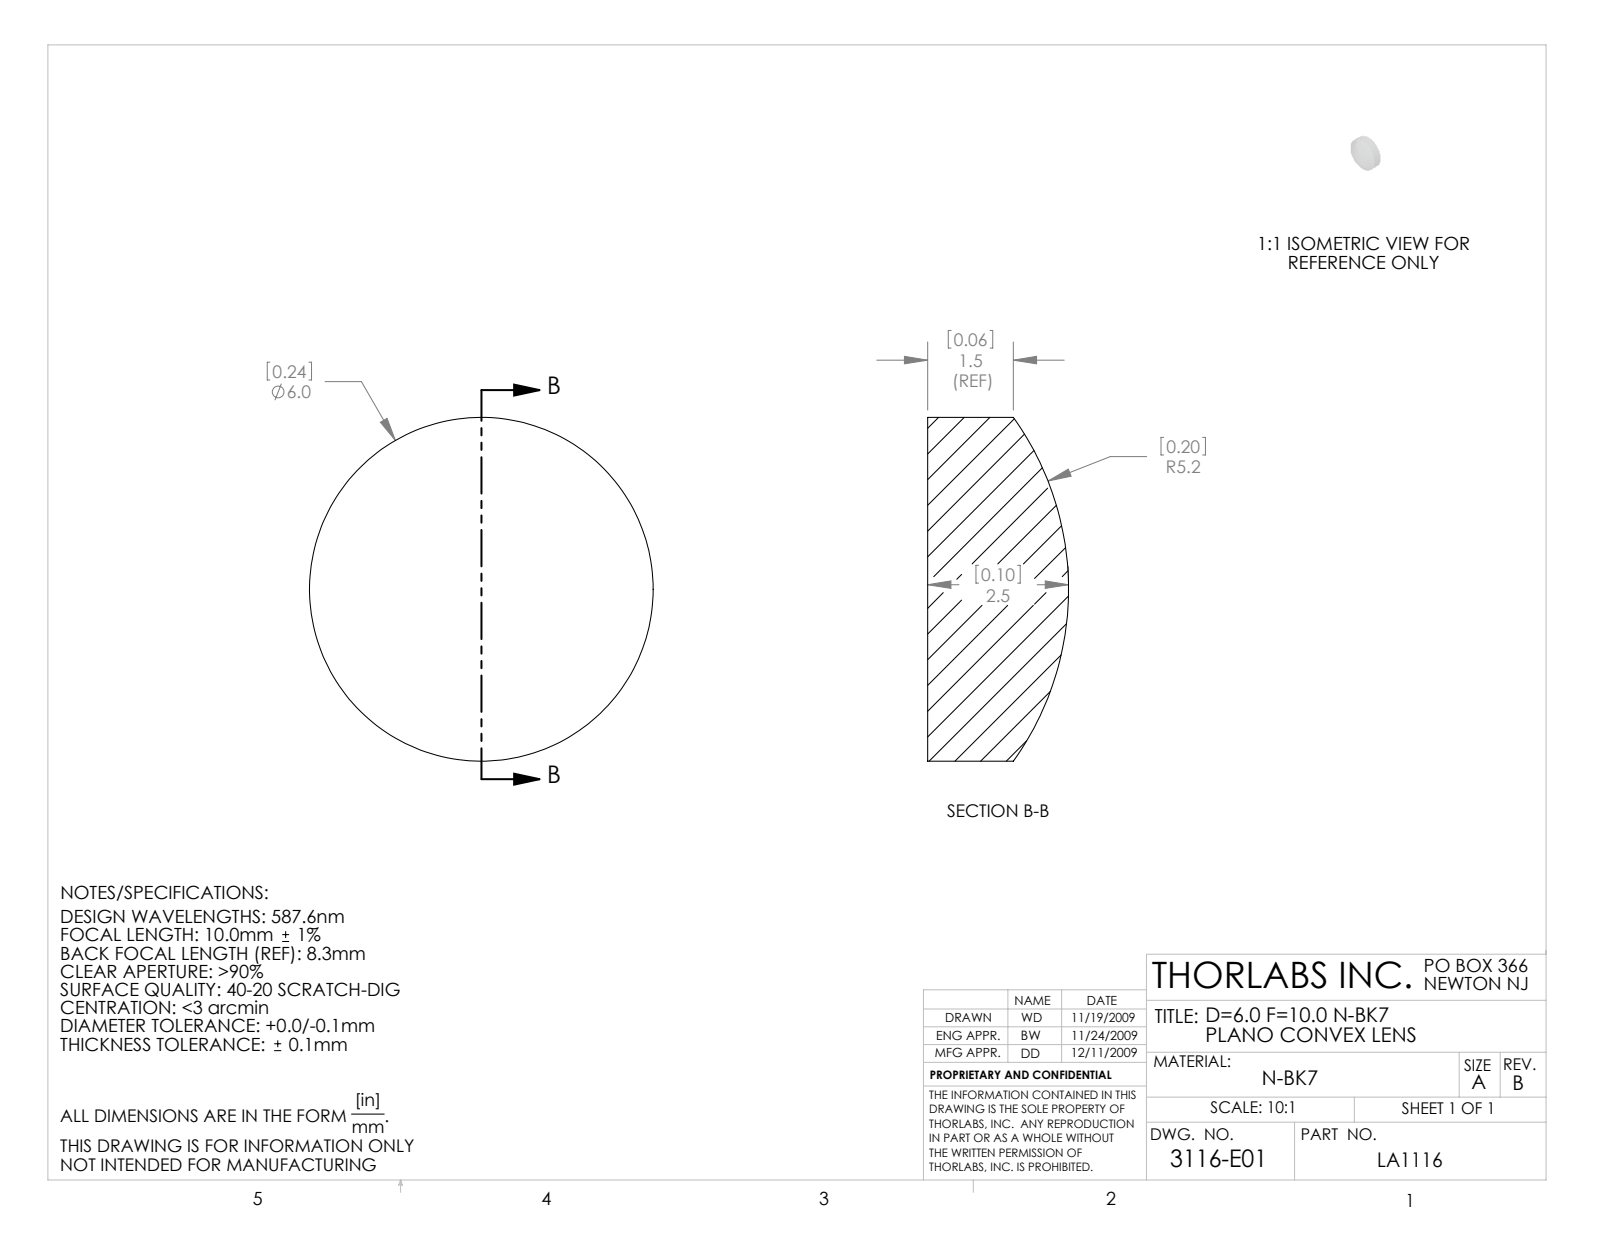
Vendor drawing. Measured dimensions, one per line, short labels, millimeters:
name: 3116-E0W
written by: SolidWorks 2009 (AUTOMOTIVE_DESIGN)
unit: mm
bodies: 1 solid, 5 faces (1 planar, 2 cylindrical, 2 other)
size: 6 × 6 × 2.46
volume: 56 mm³; area: 88 mm²
bosses: 1× ⌀6
